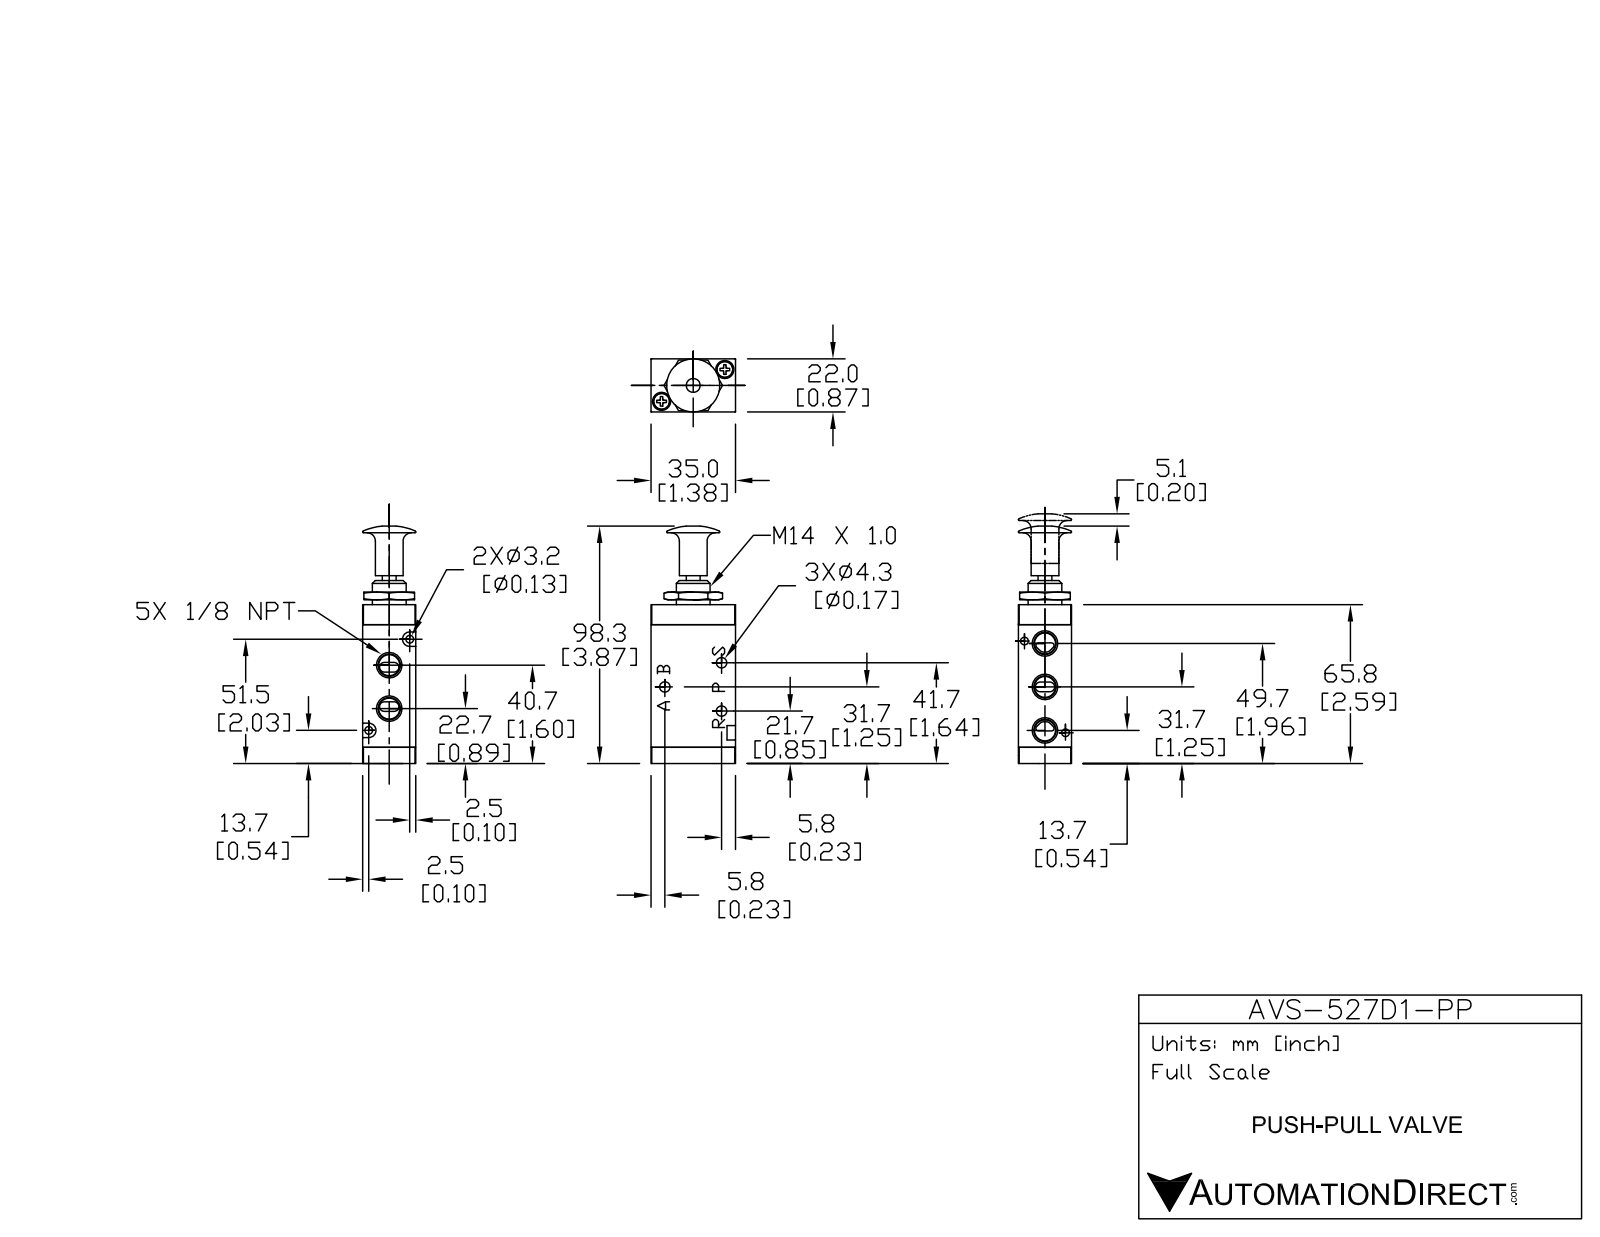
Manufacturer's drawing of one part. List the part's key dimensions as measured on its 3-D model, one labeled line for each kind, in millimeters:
Part name (STEP PRODUCT): AVS-527D1-PP
STEP written by: SolidWorks 2015 (CONFIG_CONTROL_DESIGN)
Units: millimetres
Bodies: 4 solids, 272 faces (154 planar, 68 cylindrical, 50 other)
Overall size (bounding box): 98.3 × 35 × 22
Volume: 49 110 mm³ · Surface area: 18 340 mm²
Round holes (diameter × count): ⌀4.3 ×3, ⌀3.2 ×2, ⌀7.5 ×2, ⌀5.7 ×1
Round bosses / shafts (diameter × count): ⌀6.6 ×4, ⌀6.5 ×4, ⌀22 ×1, ⌀14 ×1, ⌀11.5 ×1
Partial cylindrical surfaces — rounded edges, fillets, slot ends (radius × count): R1 ×10, R2 ×10, R3 ×2
Main face-to-face distances: 22, 50, 35, 6.7, 56.7, 8.3, 65, 58.3, 2, 5.2
Hole centre spacings: 14.7, 25.6, 20, 29.3, 41.6
